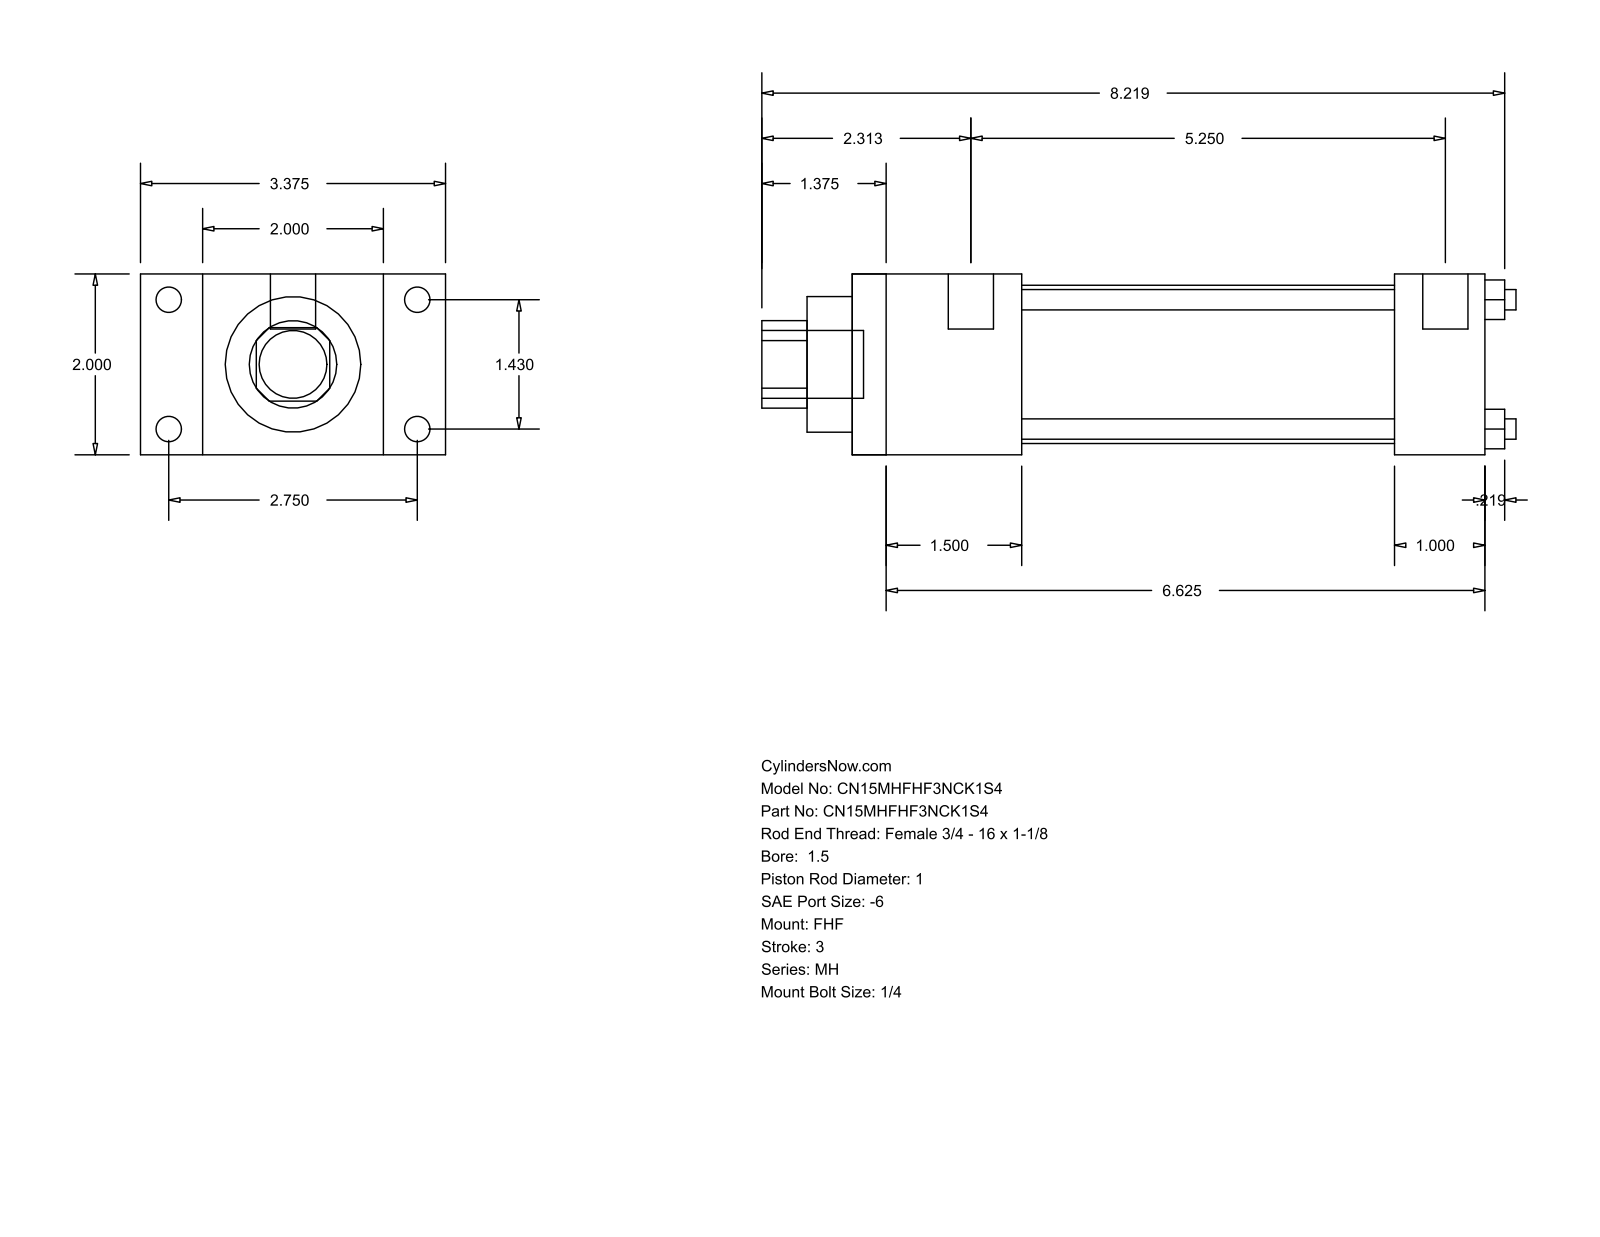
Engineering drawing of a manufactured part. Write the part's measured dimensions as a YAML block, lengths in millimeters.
part_name: "MH_FHF__0150_1"
step_written_by: "GSSL Pune (CONFIG_CONTROL_DESIGN)"
units: millimeters
bodies: {solids: 0, faces: 88, planar: 60, cylindrical: 28, other: 0}
overall_size: [211.93, 85.72, 50.8]
round_holes:
  - {diameter: 5.71, count: 4}
  - {diameter: 25.4, count: 1}
  - {diameter: 38.1, count: 1}
  - {diameter: 44.45, count: 1}
round_bosses_or_shafts:
  - {diameter: 7.14, count: 4}
  - {diameter: 5.56, count: 4}
  - {diameter: 12.7, count: 2}
  - {diameter: 19.05, count: 1}
partial_cylinders:
  - {radius: 12.29, count: 1}
face_to_face_distances: [50.8, 17.46, 68.26, 47.63, 85.72, 177.8, 130.17, 25.4, 152.4, 104.77]
hole_center_spacings: [25.68, 36.32, 51.36]
